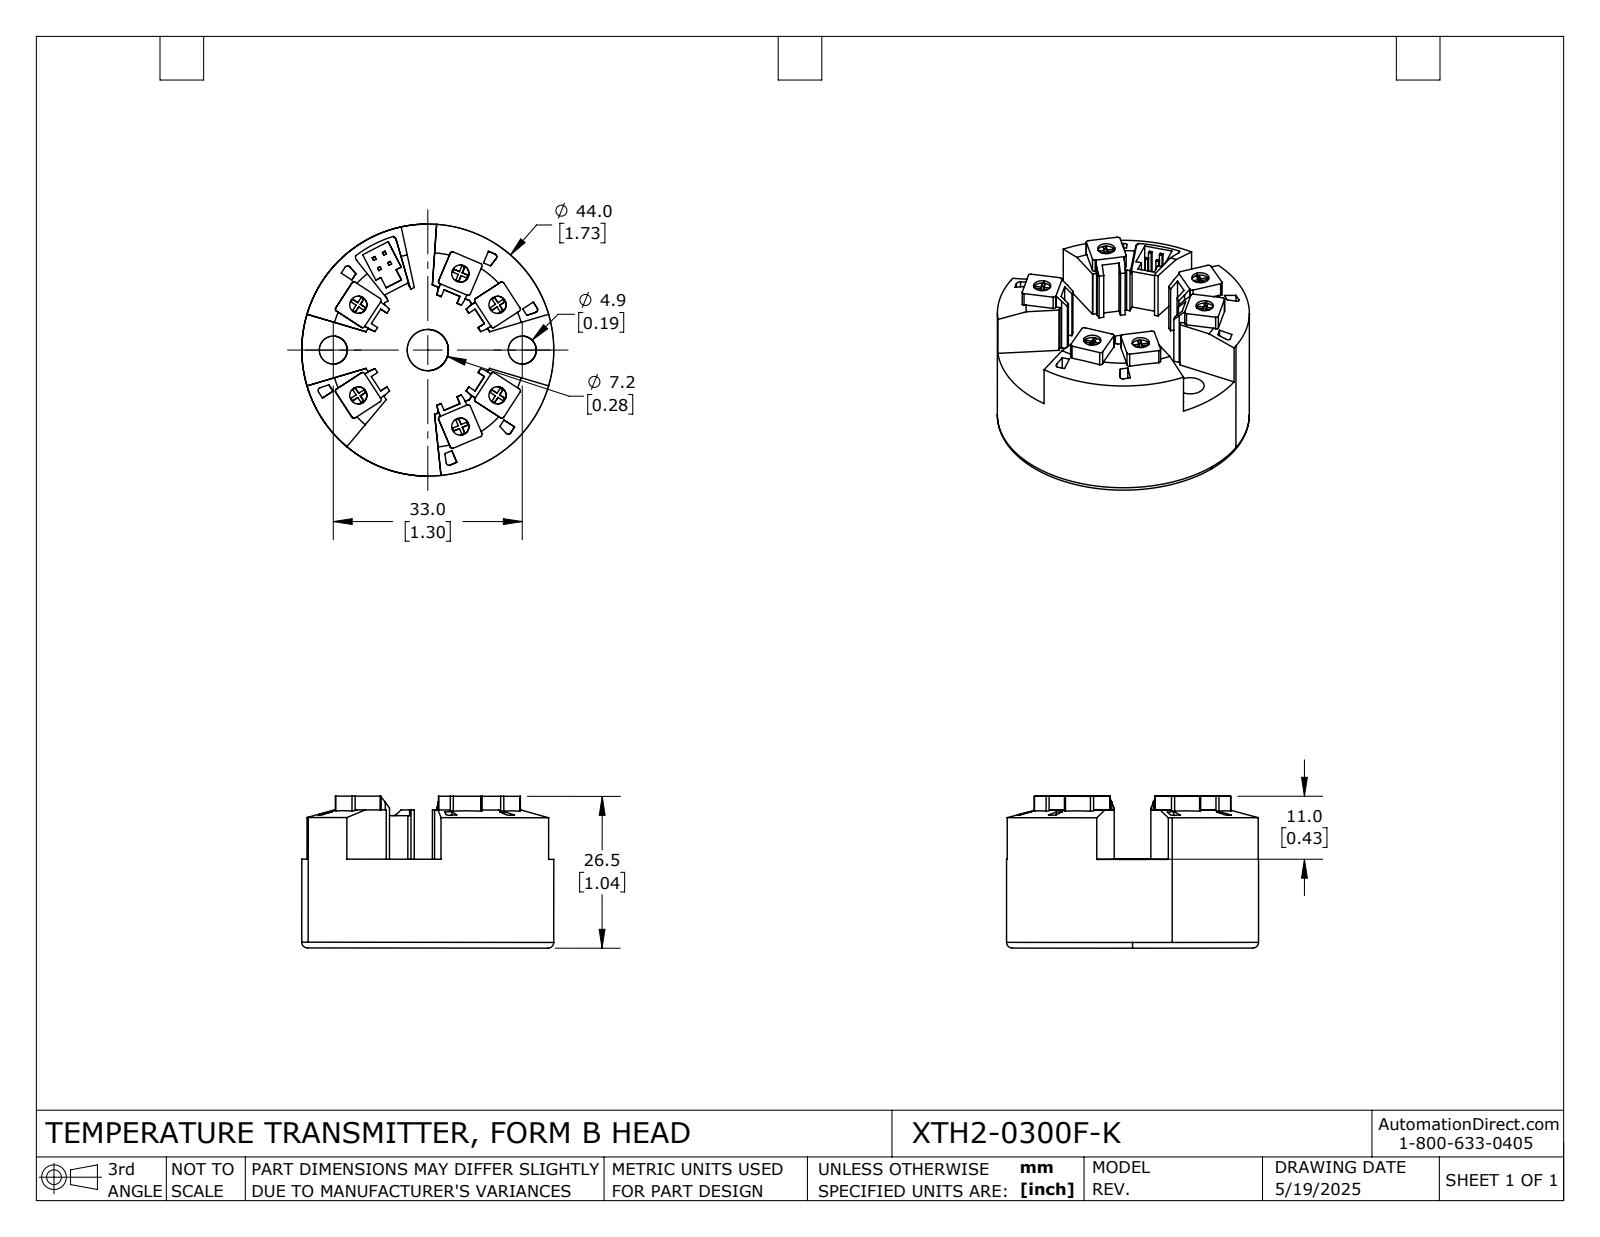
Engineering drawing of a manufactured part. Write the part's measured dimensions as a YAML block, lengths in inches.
part_name: "XTDH2-0300F-K"
step_written_by: "SolidWorks 2024 (AUTOMOTIVE_DESIGN)"
units: inches
bodies: {solids: 1, faces: 341, planar: 281, cylindrical: 52, other: 8}
overall_size: [1.733, 1.732, 1.045]
volume: 1.748
surface_area: 13.46
round_holes:
  - {diameter: 0.118, count: 6}
  - {diameter: 0.193, count: 2}
  - {diameter: 0.283, count: 1}
round_bosses_or_shafts:
  - {diameter: 1.732, count: 1}
partial_cylinders:
  - {radius: 0.016, count: 24}
  - {radius: 0.02, count: 6}
  - {radius: 0.039, count: 2}
face_to_face_distances: [0.61, 1.043, 0.433, 0.059, 0.177, 0.039, 0.02, 0.118, 0.949, 0.339]
hole_center_spacings: [0.571, 0.333, 0.355, 0.356, 0.65, 0.677, 0.733, 0.875]
